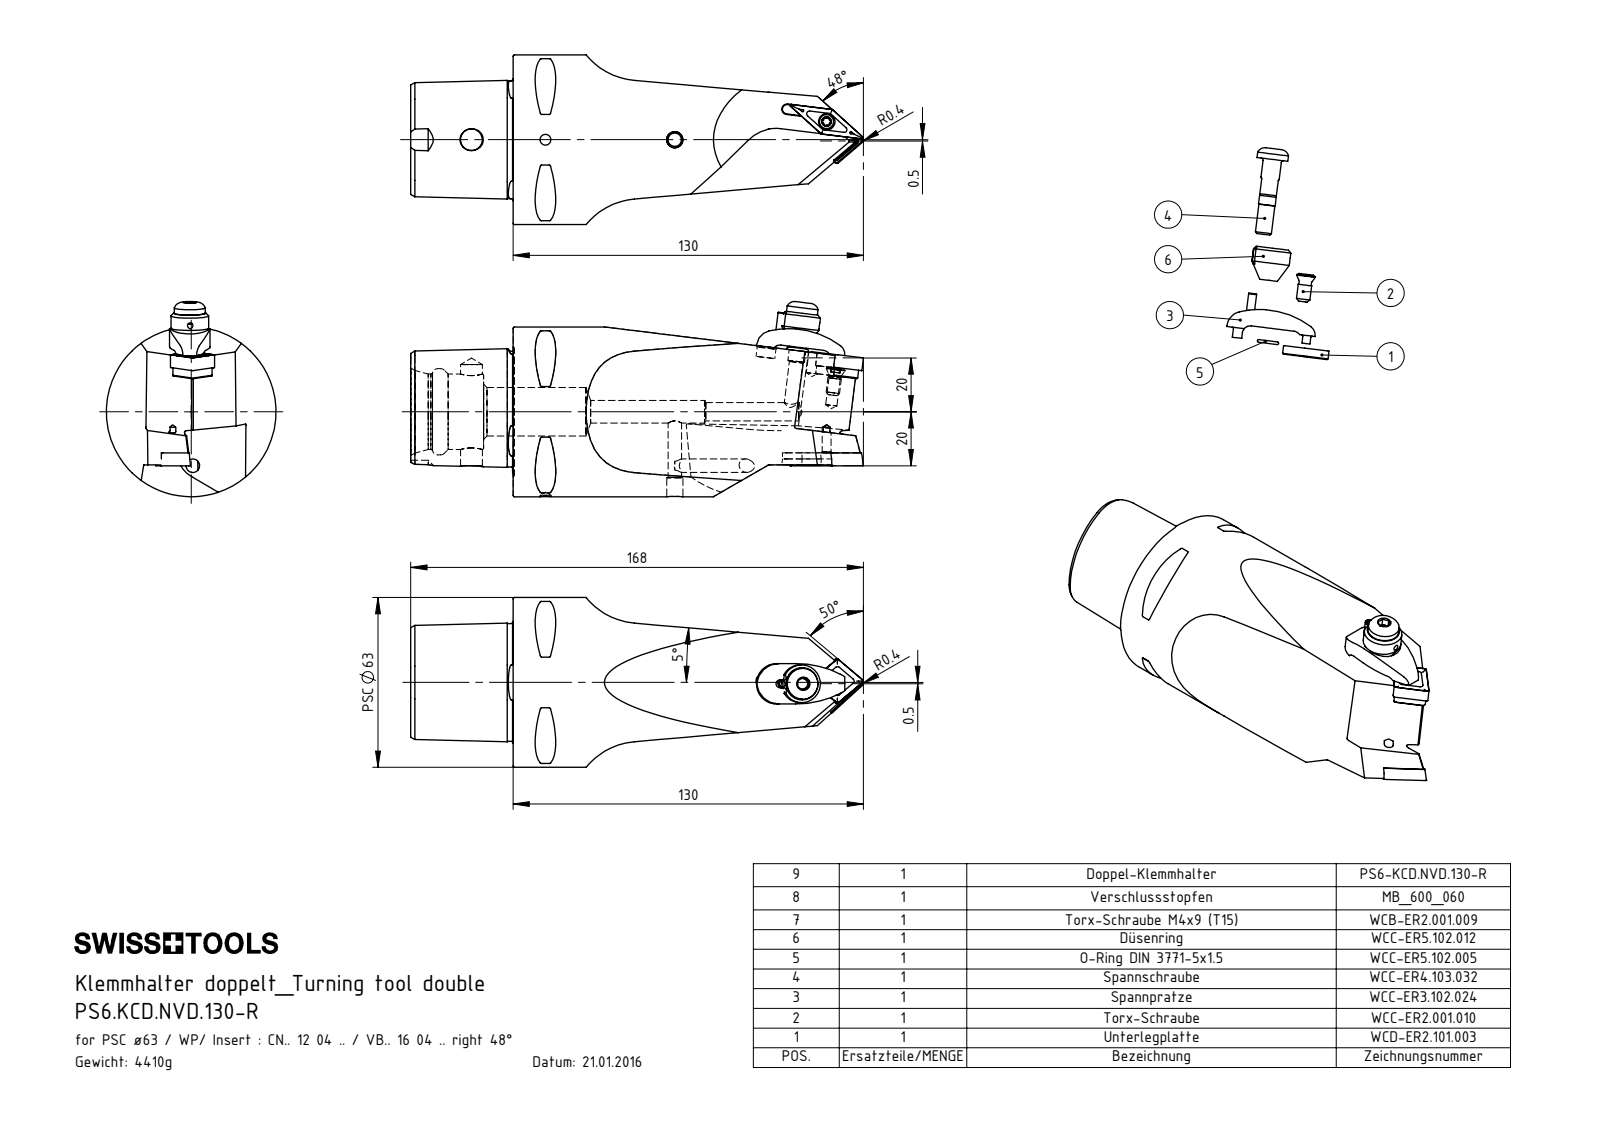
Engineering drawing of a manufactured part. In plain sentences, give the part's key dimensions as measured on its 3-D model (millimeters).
The part is named "KVT_MB_600_060; WCC-ER5.102.005_A; PS6.KCD.NVD.130-R; ISO 13337 - 3 x 12_PreviewCfg (+8 more)". Its 3-D file was written by "SolidWorks 2017 (AUTOMOTIVE_DESIGN)". It is 13 solids with 553 faces: 133 planar, 171 cylindrical and 249 other. Overall it measures 168.81 by 72.45 by 63 millimeters. Its volume is 283 139 cubic millimeters and its surface area 45 342 square millimeters. Round holes: 3 of diameter 2, 3 of diameter 5, 2 of diameter 4.2, 2 of diameter 6.2, 2 of diameter 7, 1 of diameter 2.4, 1 of diameter 3, 1 of diameter 3.3, 1 of diameter 4, 1 of diameter 4.4, 1 of diameter 5.16, 1 of diameter 6.1. Round bosses or shafts: 2 of diameter 6, 2 of diameter 4, 2 of diameter 3, 1 of diameter 63, 1 of diameter 14, 1 of diameter 11.5, 1 of diameter 7, 1 of diameter 6.8. Partial cylindrical surfaces (rounded edges, fillets, slot ends): 11 of radius 0.5, 6 of radius 0.34, 6 of radius 0.39, 6 of radius 0.59, 4 of radius 0.4, 4 of radius 1, 3 of radius 0.69, 3 of radius 0.69. The main face-to-face distances are 38, 4.46, 24.88, 11, 27, 12.7, 11.49, 1.3, 5.76, 3.18. The hole center spacings are 8, 6.36, 7.99, 14.94, 15, 6.16, 6.37, 8.01.
